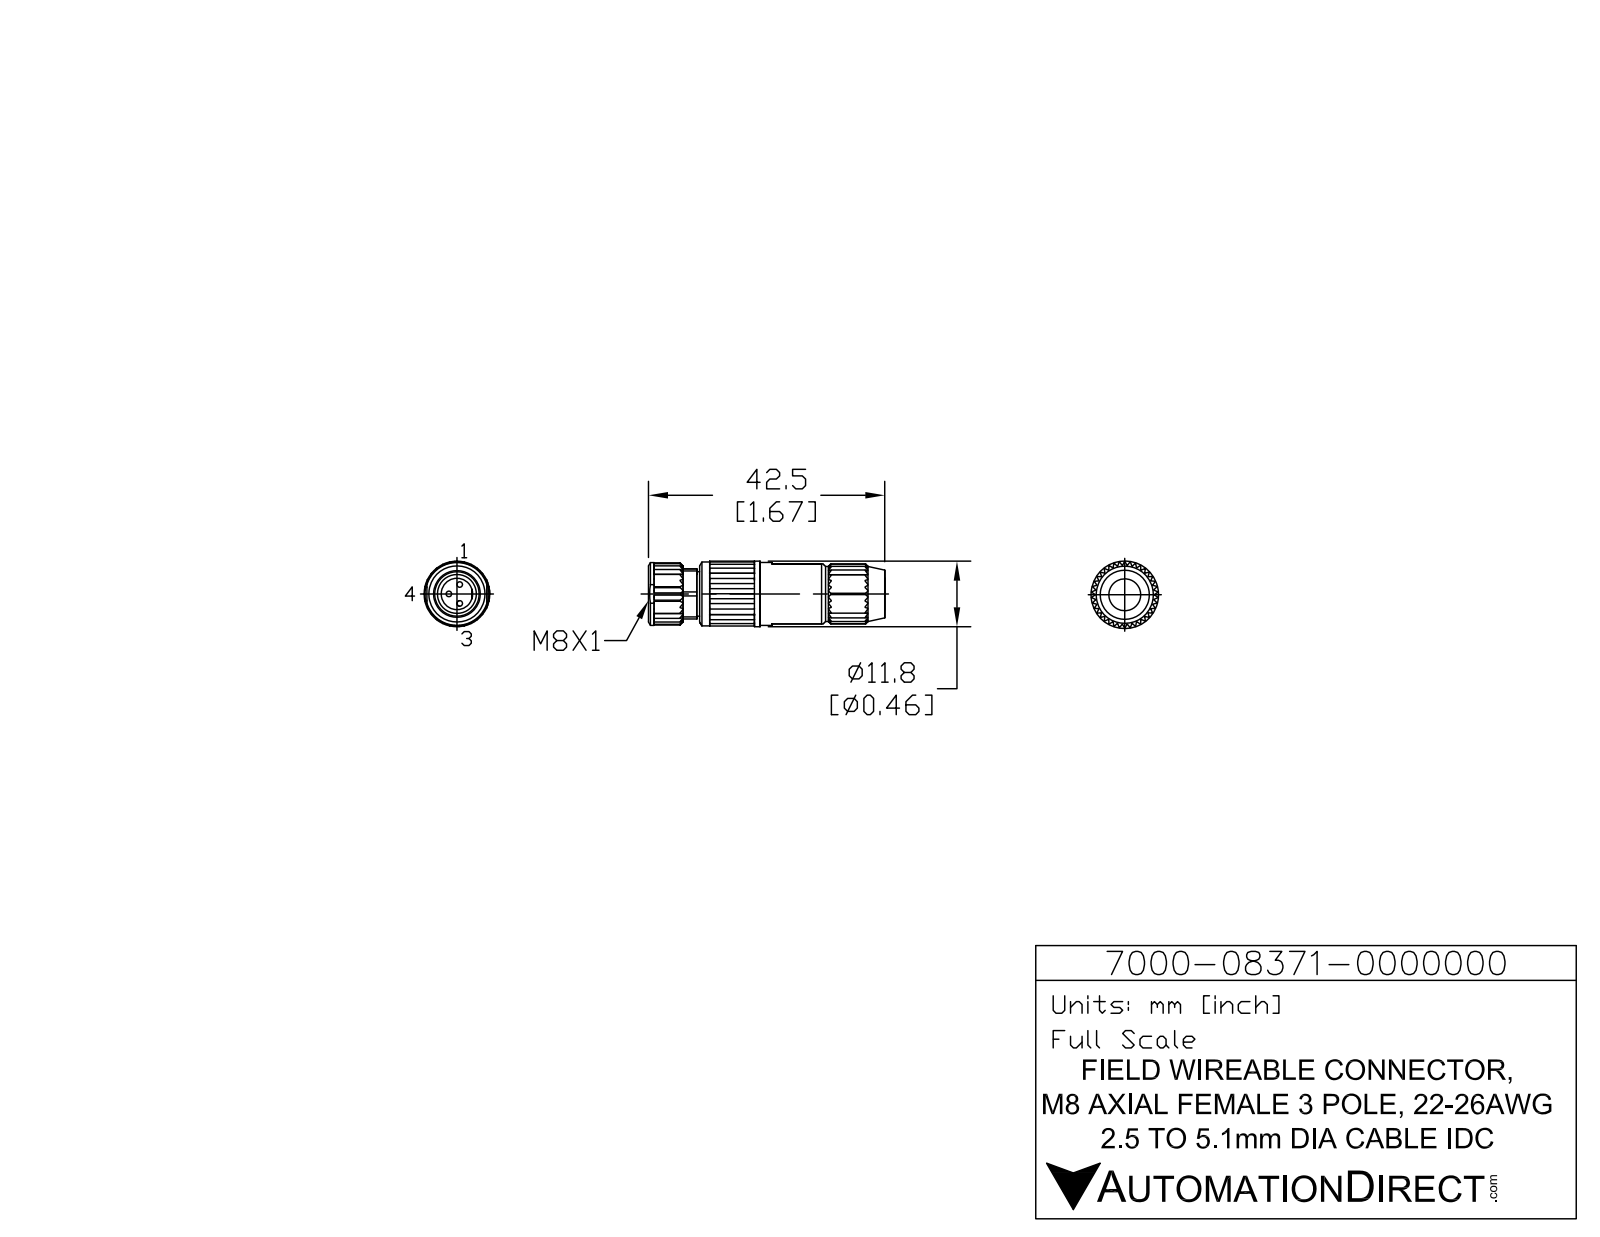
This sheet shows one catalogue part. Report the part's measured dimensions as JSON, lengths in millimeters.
{"part_name": "7000-08371-0000000", "step_written_by": "SolidWorks 2015 (AUTOMOTIVE_DESIGN)", "units": "millimeters", "bodies": {"solids": 1, "faces": 393, "planar": 321, "cylindrical": 20, "other": 52}, "overall_size": [42.5, 11.8, 11.8], "volume_mm3": 3647, "surface_area_mm2": 3118, "round_holes": [[1, 3], [5.58, 1], [6.76, 1]], "round_bosses_or_shafts": [[11.8, 1], [11.74, 1], [10, 1], [5.7, 1]], "face_to_face_distances": [5.6, 5.58, 8.9, 42.5, 33.8, 8.7, 12.9, 1.66, 7.24, 10.5], "hole_center_spacings": [1.59, 2.34, 1.26, 3]}
